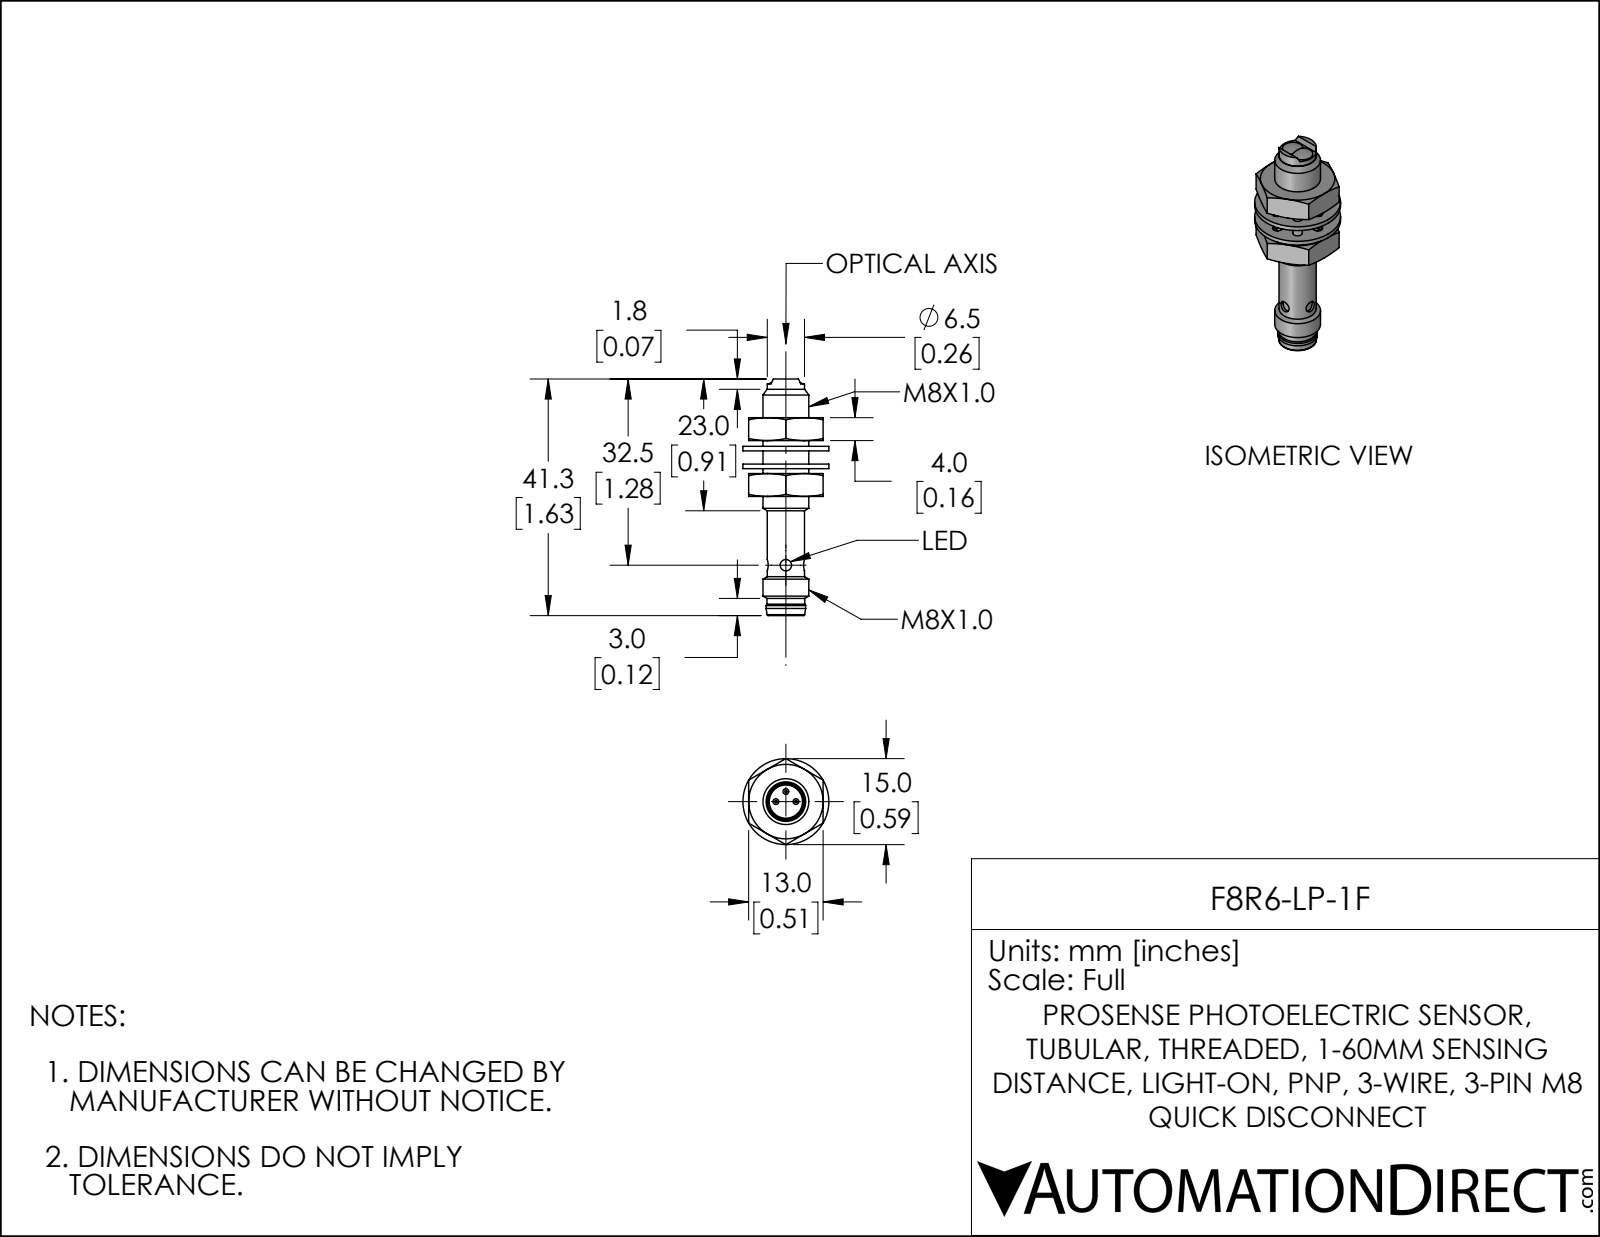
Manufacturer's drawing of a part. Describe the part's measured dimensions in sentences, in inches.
The part is named "F8R6-LP-1F". Its 3-D file was written by "SolidWorks 2019 (CONFIG_CONTROL_DESIGN)". It is 5 solids with 157 faces: 63 planar, 54 cylindrical and 40 other. Overall it measures 1.626 by 0.591 by 0.591 inches. Its volume is 0.162 cubic inches and its surface area 4.169 square inches. Round holes: 2 of diameter 0.079, 1 of diameter 0.228, 1 of diameter 0.272. Round bosses or shafts: 3 of diameter 0.039, 1 of diameter 0.591, 1 of diameter 0.315, 1 of diameter 0.272, 1 of diameter 0.26, 1 of diameter 0.256. Partial cylindrical surfaces (rounded edges, fillets, slot ends): 8 of radius 0.032, 1 of radius 0.109, 1 of radius 0.165. The main face-to-face distances are 0.122, 0.031, 0.512, 0.384, 0.157, 0.154, 0.091, 0.033, 0.065, 0.197.
